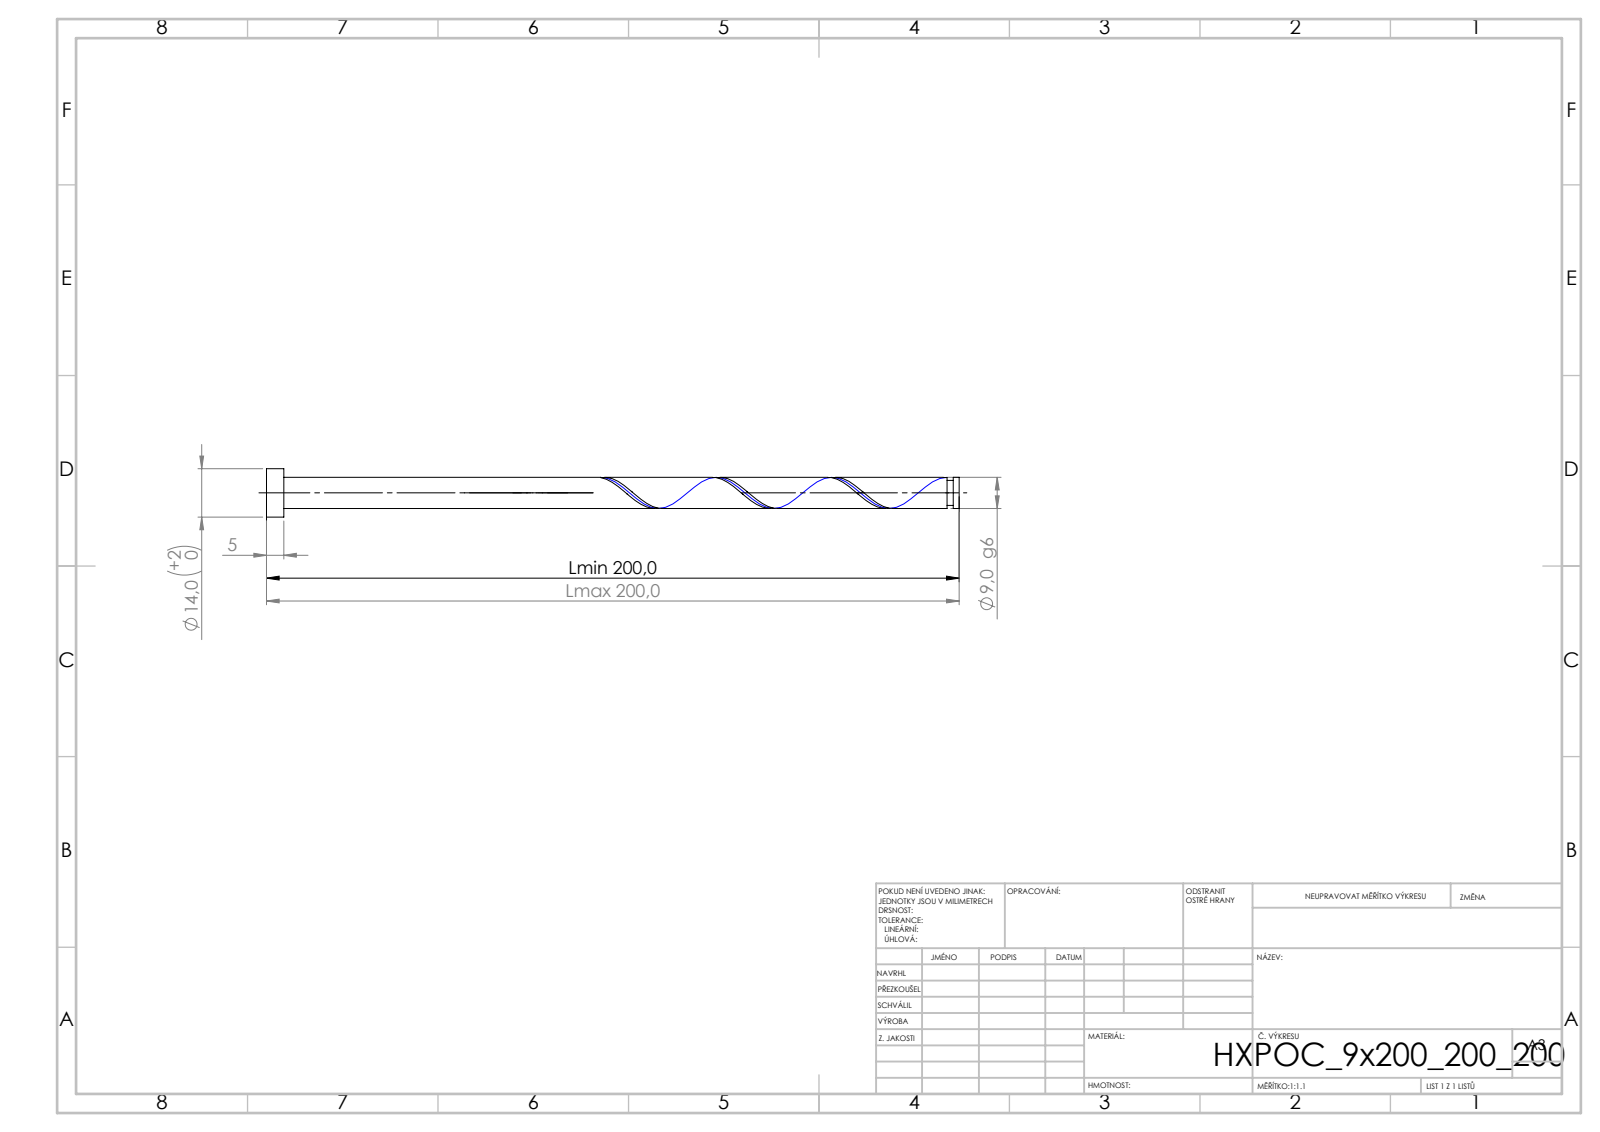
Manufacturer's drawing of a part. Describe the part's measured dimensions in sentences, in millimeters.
Its 3-D file was written by "SolidWorks 2019 (CONFIG_CONTROL_DESIGN)". It is 1 solid with 21 faces: 6 planar, 14 cylindrical and 1 other. Overall it measures 200 by 14 by 14 millimeters. Its volume is 13 012 cubic millimeters and its surface area 6 201 square millimeters. Round bosses or shafts: 1 of diameter 14, 1 of diameter 9, 1 of diameter 7.2. The main face-to-face distances are 5, 200, 195, 198.3, 193.3, 1.7, 196.5, 191.5, 1.8, 3.5.
